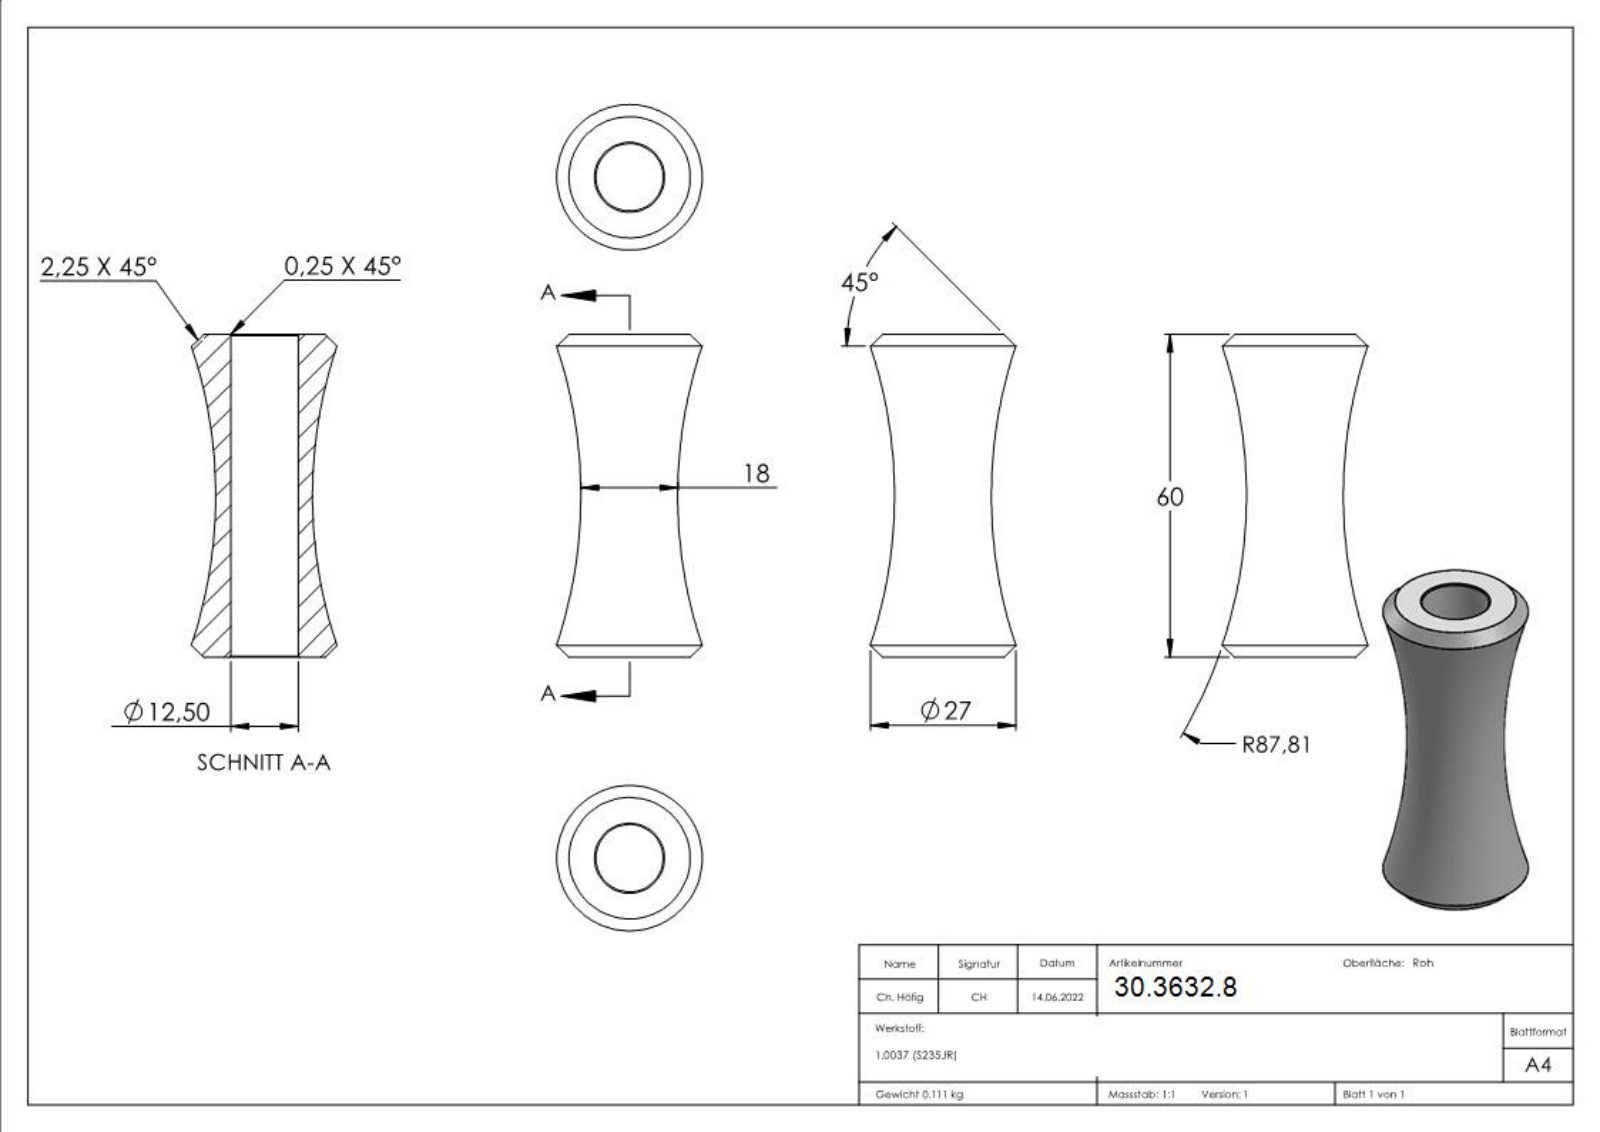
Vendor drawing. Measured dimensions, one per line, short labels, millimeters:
name: 1385-ST
written by: SolidWorks 2018 (CONFIG_CONTROL_DESIGN)
unit: mm
bodies: 1 solid, 256 faces (107 planar, 22 cylindrical, 127 other)
size: 60 × 27 × 27
volume: 14 282 mm³; area: 7 124 mm²
holes: 1× ⌀12.5
rounds: 1× R6.35
face distances: 60, 0.34, 2.45, 2.24, 0.32, 2.2, 2.9, 2.61, 1.96, 0.96
